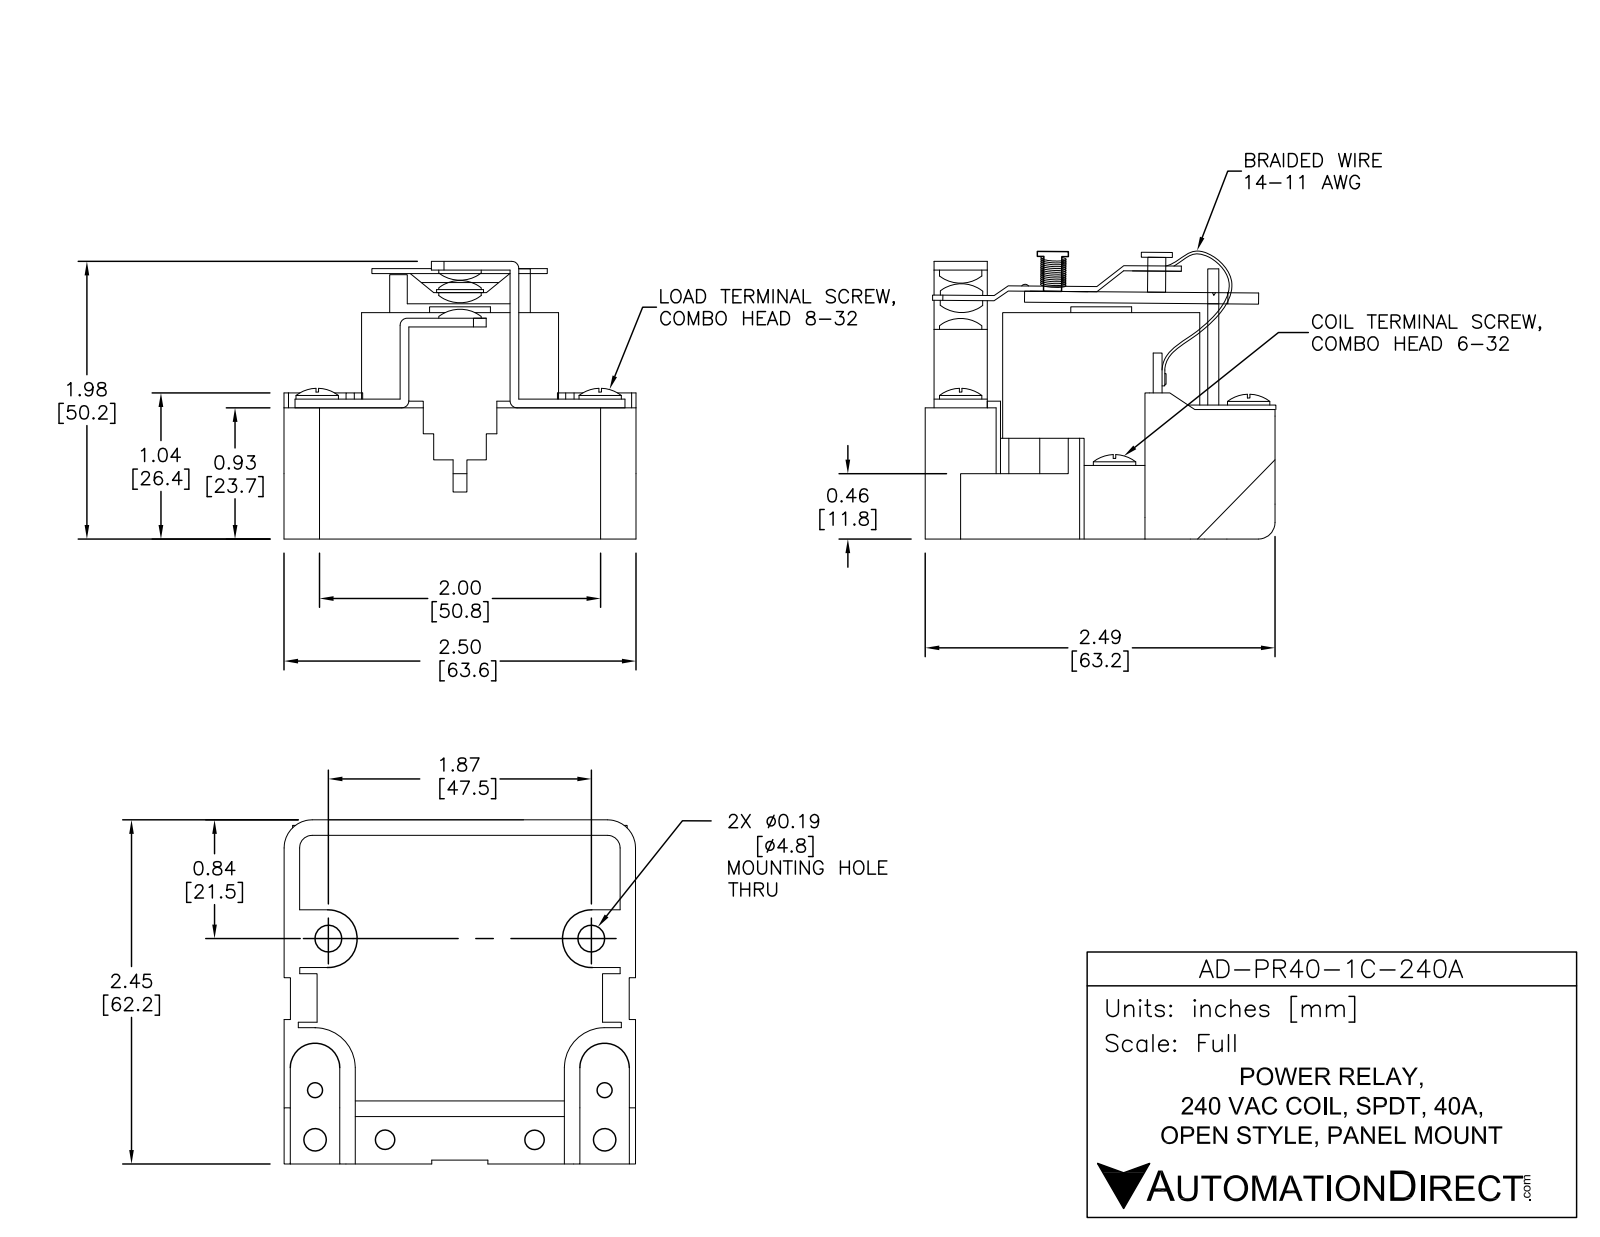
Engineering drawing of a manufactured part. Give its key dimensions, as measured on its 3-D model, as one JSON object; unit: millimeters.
{"part_name": "AD-PR40-1C-240A", "step_written_by": "SolidWorks 2013 (AUTOMOTIVE_DESIGN)", "units": "millimeters", "bodies": {"solids": 35, "faces": 642, "planar": 422, "cylindrical": 128, "other": 92}, "overall_size": [64.94, 64.1, 51.55], "volume_mm3": 91031, "surface_area_mm2": 33438, "round_holes": [[5, 4], [2.5, 2], [3.33, 2], [10, 2], [30, 1]], "round_bosses_or_shafts": [[7.75, 3], [6.85, 2], [5.28, 2], [35.5, 1], [18, 1], [10, 1], [6.5, 1], [5.5, 1]], "partial_cylinders_radius": [[0.75, 10], [3, 6], [0.38, 4], [1, 4], [1.48, 4], [1.5, 4], [2, 3], [0.5, 2]], "face_to_face_distances": [12, 2, 10, 64, 32.75, 1.75, 1, 1.5, 30.75, 6.5], "hole_center_spacings": [10, 26.2, 27.51, 29.92, 36.54, 37.51, 49.24, 50.25]}
